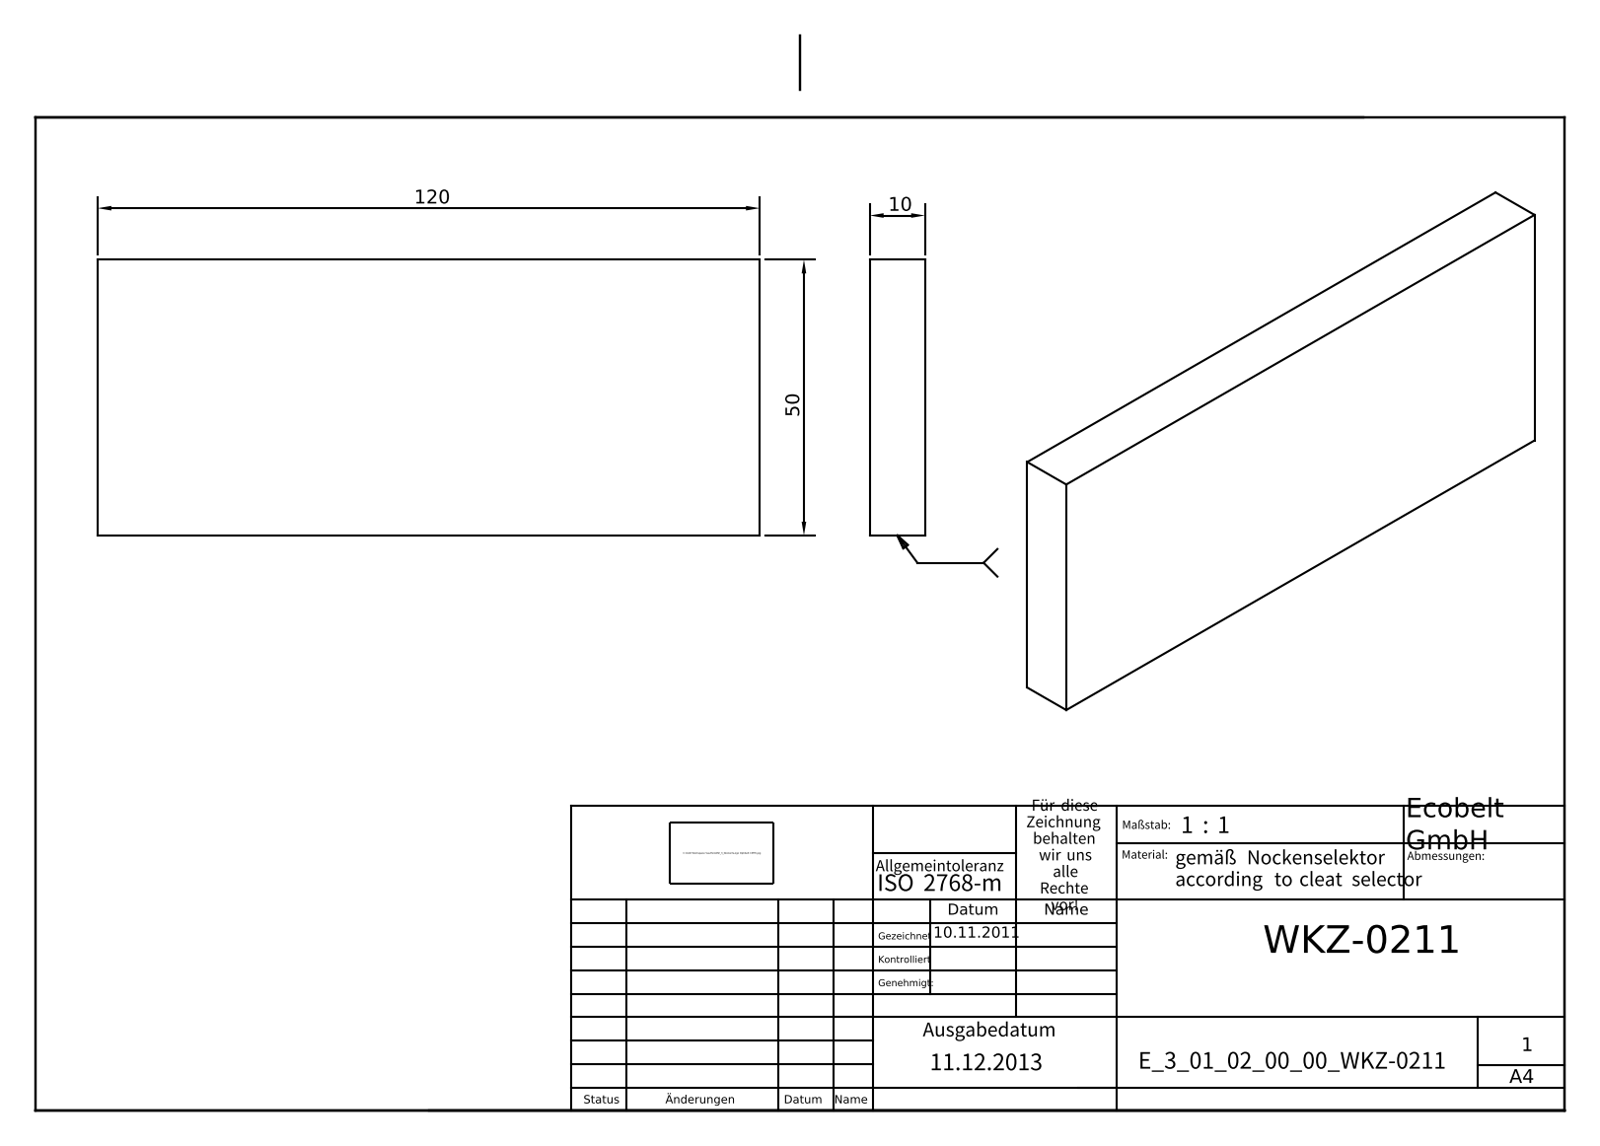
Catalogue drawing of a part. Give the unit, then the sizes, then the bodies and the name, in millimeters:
Units: millimetres
Overall size (bounding box): 120 × 50 × 10
Main face-to-face distances: 10, 50, 120
Volume: 60 000 mm³ · Surface area: 15 400 mm²
Bodies: 1 solid, 6 faces (6 planar, 0 cylindrical, 0 other)
Part name (STEP PRODUCT): E_3_01_02_00_00_WKZ-0211
STEP written by: Autodesk Inventor 2021 (AUTOMOTIVE_DESIGN)
